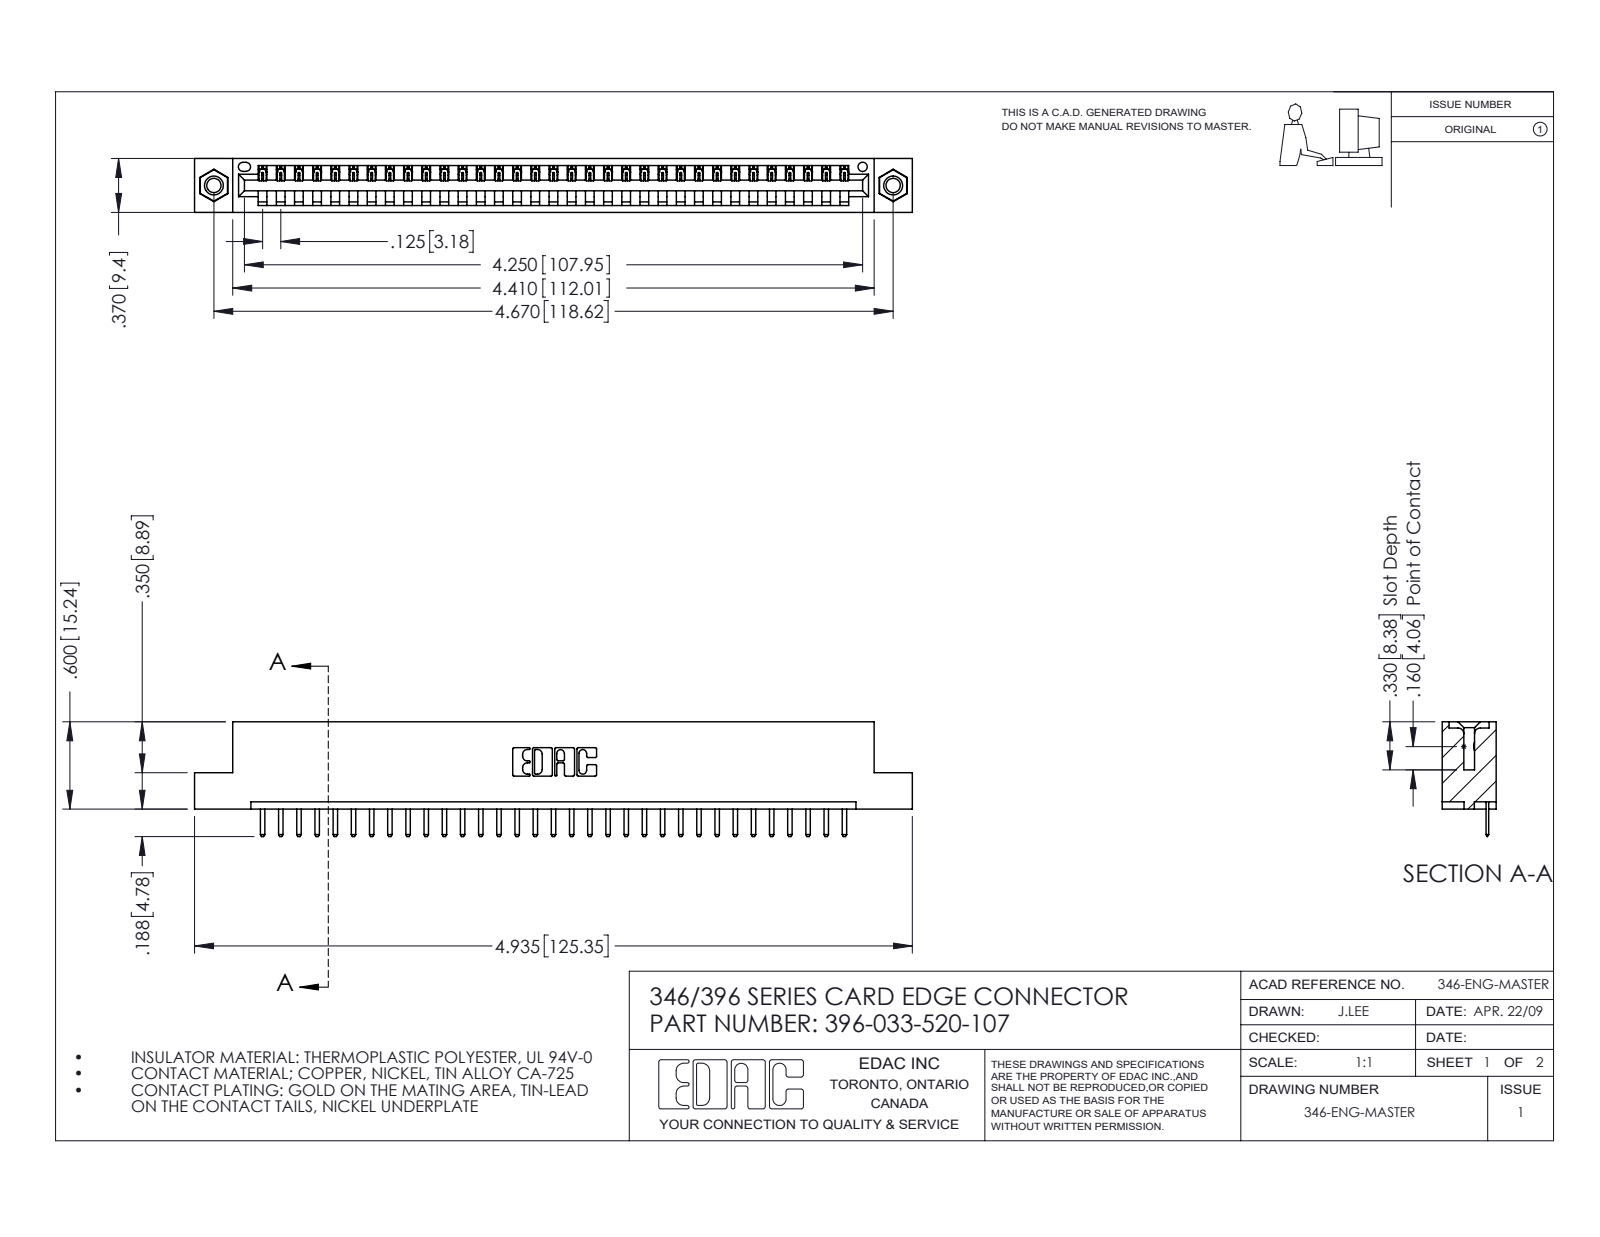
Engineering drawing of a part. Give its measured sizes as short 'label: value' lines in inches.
name: 345-250-001_345-250-005-103; 396-033-520-107; 346 Part_Flush Mounting Lugs - 0.156 Dia-TI; 345-292-001_345-293-120
written by: SolidWorks 2016 (CONFIG_CONTROL_DESIGN)
unit: in
bodies: 36 solids, 2228 faces (1494 planar, 718 cylindrical, 16 other)
size: 4.935 × 0.788 × 0.37
volume: 0.722 in³; area: 22.33 in²
holes: 2× ⌀0.098, 2× ⌀0.125, 2× ⌀0.156, 1× ⌀0.064
bosses: 2× ⌀0.155
rounds: 68× R0.01, 66× R0.006, 22× R0.01, 6× R0.007, 6× R0.031, 3× R0.026, 2× R0.031, 2× R0.04
face distances: 0.048, 0.322, 0.37, 0.25, 0.148, 0.222, 0.1, 0.174, 0.072, 0.298
hole spacings: 0.246, 4.462, 4.67
